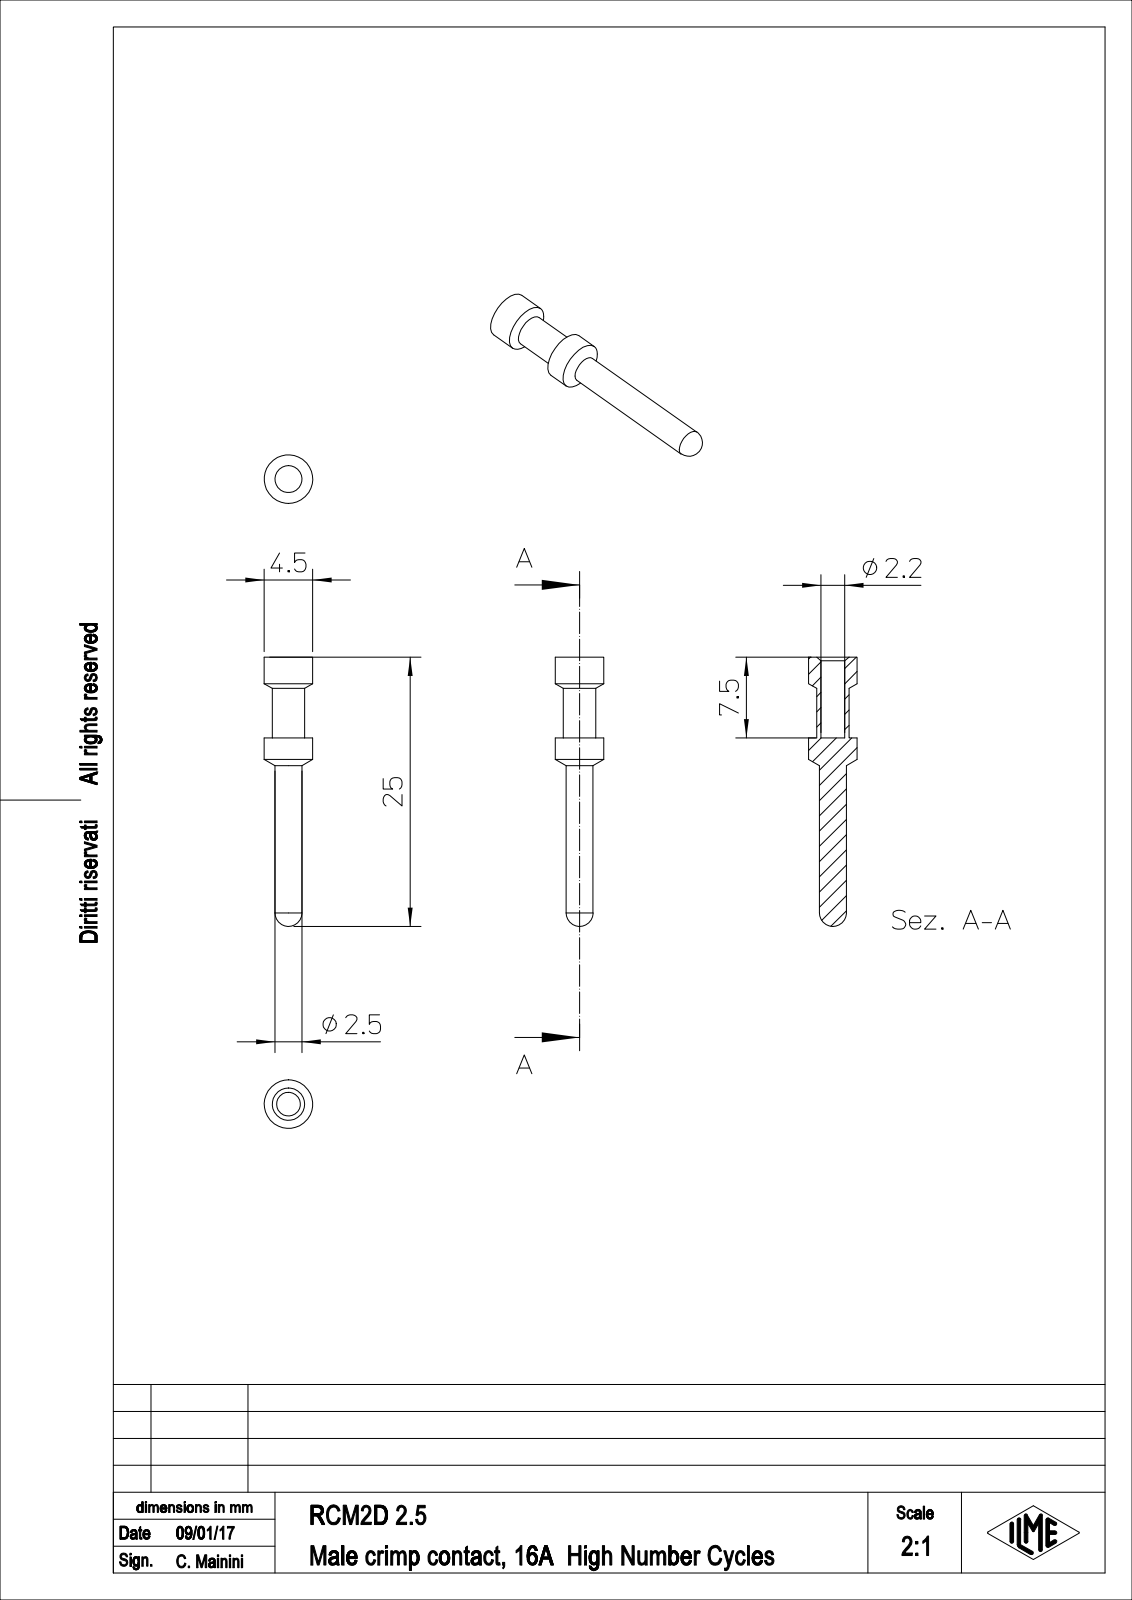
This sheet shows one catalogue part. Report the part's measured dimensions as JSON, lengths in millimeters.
{"part_name": "RCM2D_2.5", "step_written_by": "PTC Creo Elements/Direct Modeling 19.0E 27-Jun-2016 (C) Parametric Technology GmbH (AUTOMOTIVE_DESIGN)", "units": "millimeters", "bodies": {"solids": 1, "faces": 21, "planar": 3, "cylindrical": 10, "other": 8}, "overall_size": [25, 4.5, 4.5], "volume_mm3": 156, "surface_area_mm2": 322, "round_holes": [[2.2, 1]], "round_bosses_or_shafts": [[4.5, 1], [3, 1], [2.5, 1]], "face_to_face_distances": [7.5]}
